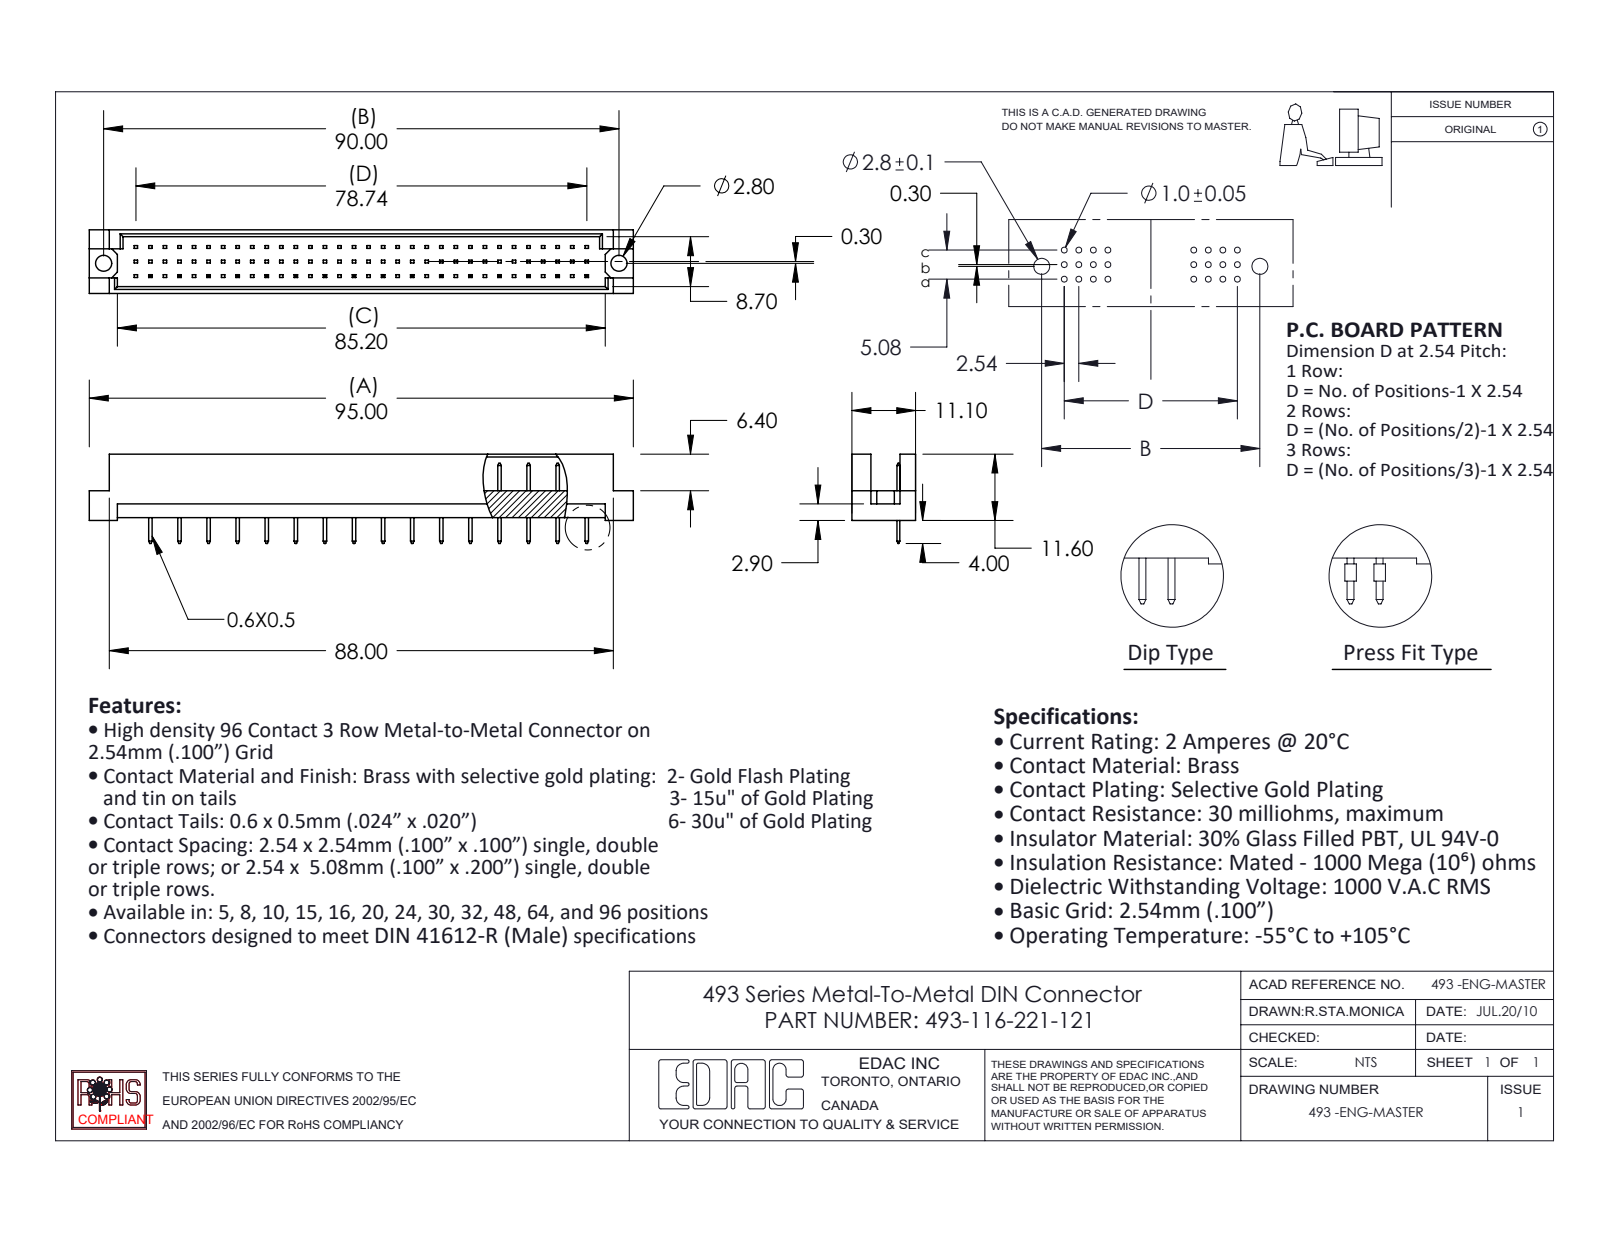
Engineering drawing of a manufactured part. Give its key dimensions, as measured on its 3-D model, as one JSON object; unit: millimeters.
{"part_name": "493-116-221-122; 493-290_21; 493 Part_96", "step_written_by": "SolidWorks 2020 (CONFIG_CONTROL_DESIGN)", "units": "millimeters", "bodies": {"solids": 17, "faces": 660, "planar": 656, "cylindrical": 4, "other": 0}, "overall_size": [95, 15.6, 11.1], "volume_mm3": 5725, "surface_area_mm2": 6961, "round_holes": [[2.8, 2]], "face_to_face_distances": [1.2, 9.9, 11.1, 8.7, 4.7, 0.5, 5.08, 2.54, 2.76, 3.26], "hole_center_spacings": [90]}
